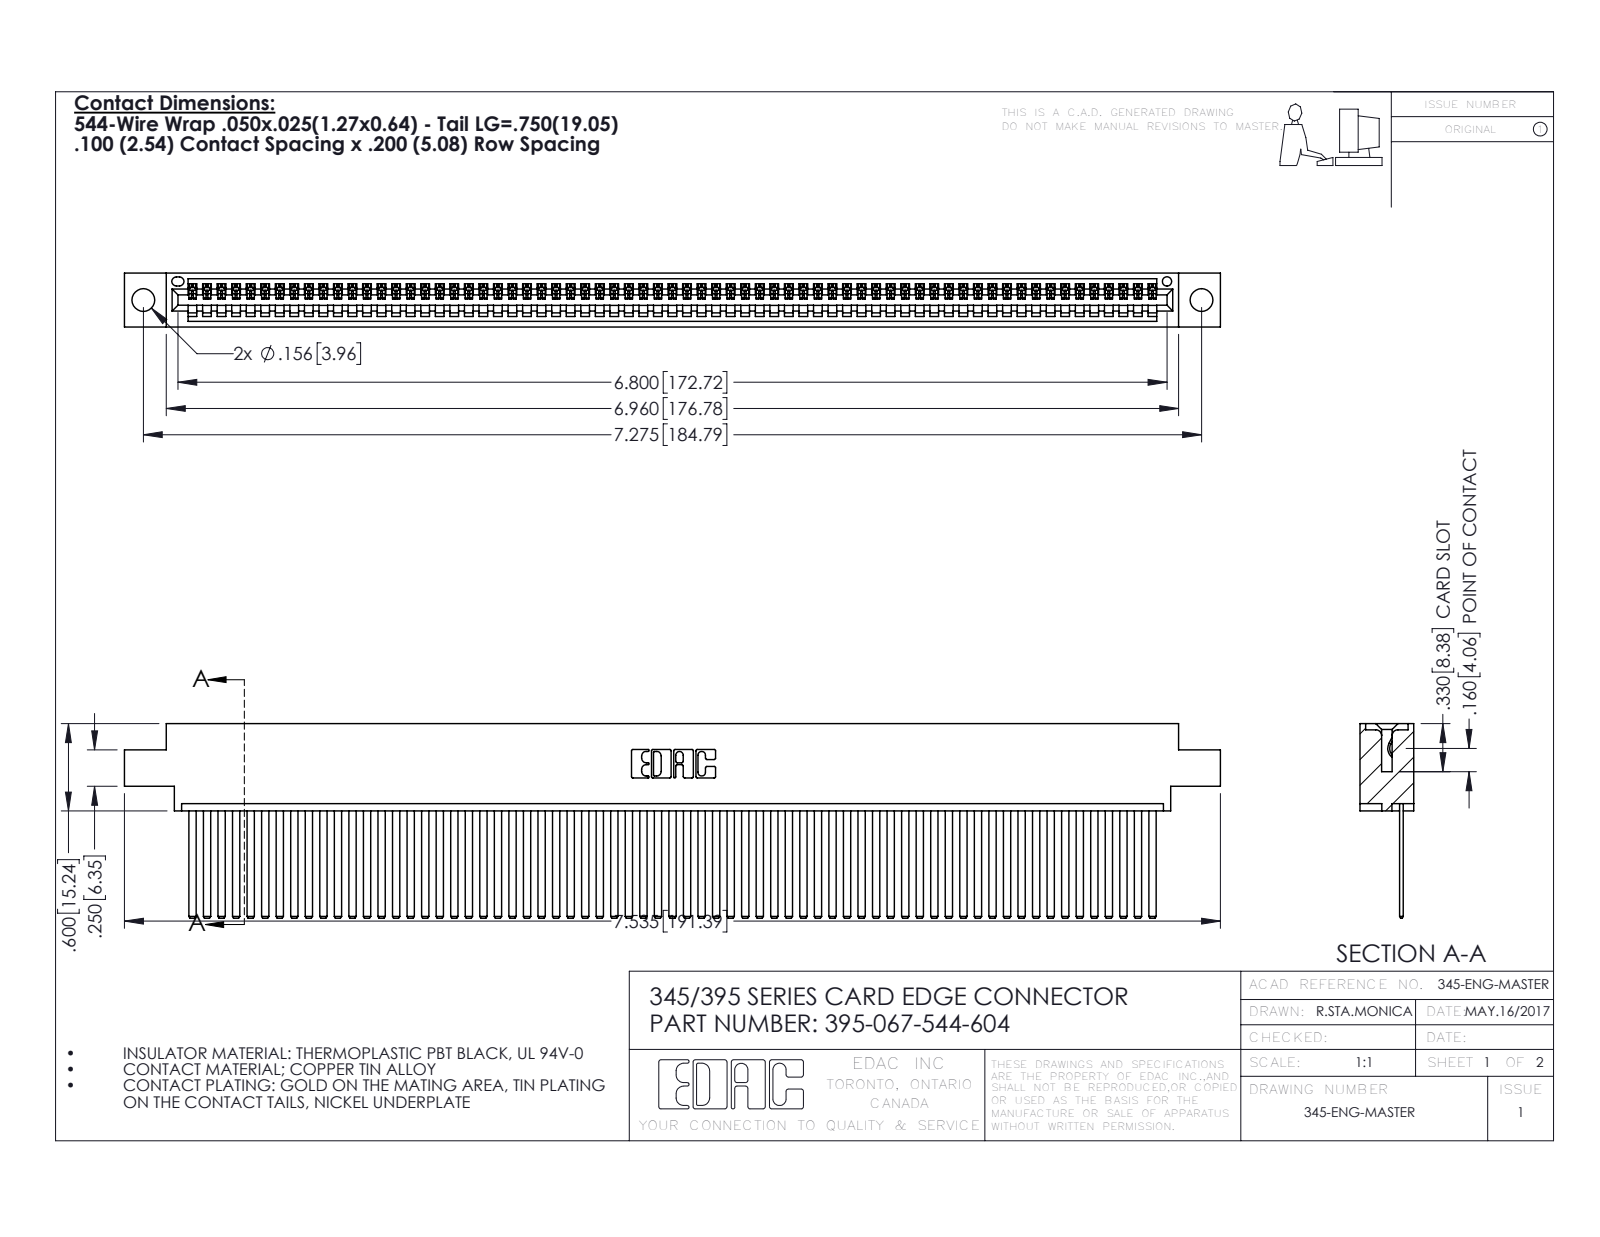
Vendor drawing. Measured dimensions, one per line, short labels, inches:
name: 345-292-001_345-293-144; 395-067-544-604; 345 Part_0.170 Offset - 0.156 Dia-TH
written by: SolidWorks 2016 (CONFIG_CONTROL_DESIGN)
unit: in
bodies: 68 solids, 3614 faces (2496 planar, 1118 cylindrical, 0 other)
size: 7.535 × 1.337 × 0.37
volume: 1.157 in³; area: 43.09 in²
holes: 2× ⌀0.156, 1× ⌀0.064
rounds: 134× R0.006, 22× R0.01, 6× R0.007, 6× R0.031, 3× R0.026, 2× R0.031, 2× R0.04, 1× R0.014
face distances: 0.072, 0.298, 0.025, 0.098, 0.272, 0.37, 0.2, 0.225, 0.175, 0.149
hole spacings: 0.27, 7.039, 7.275
